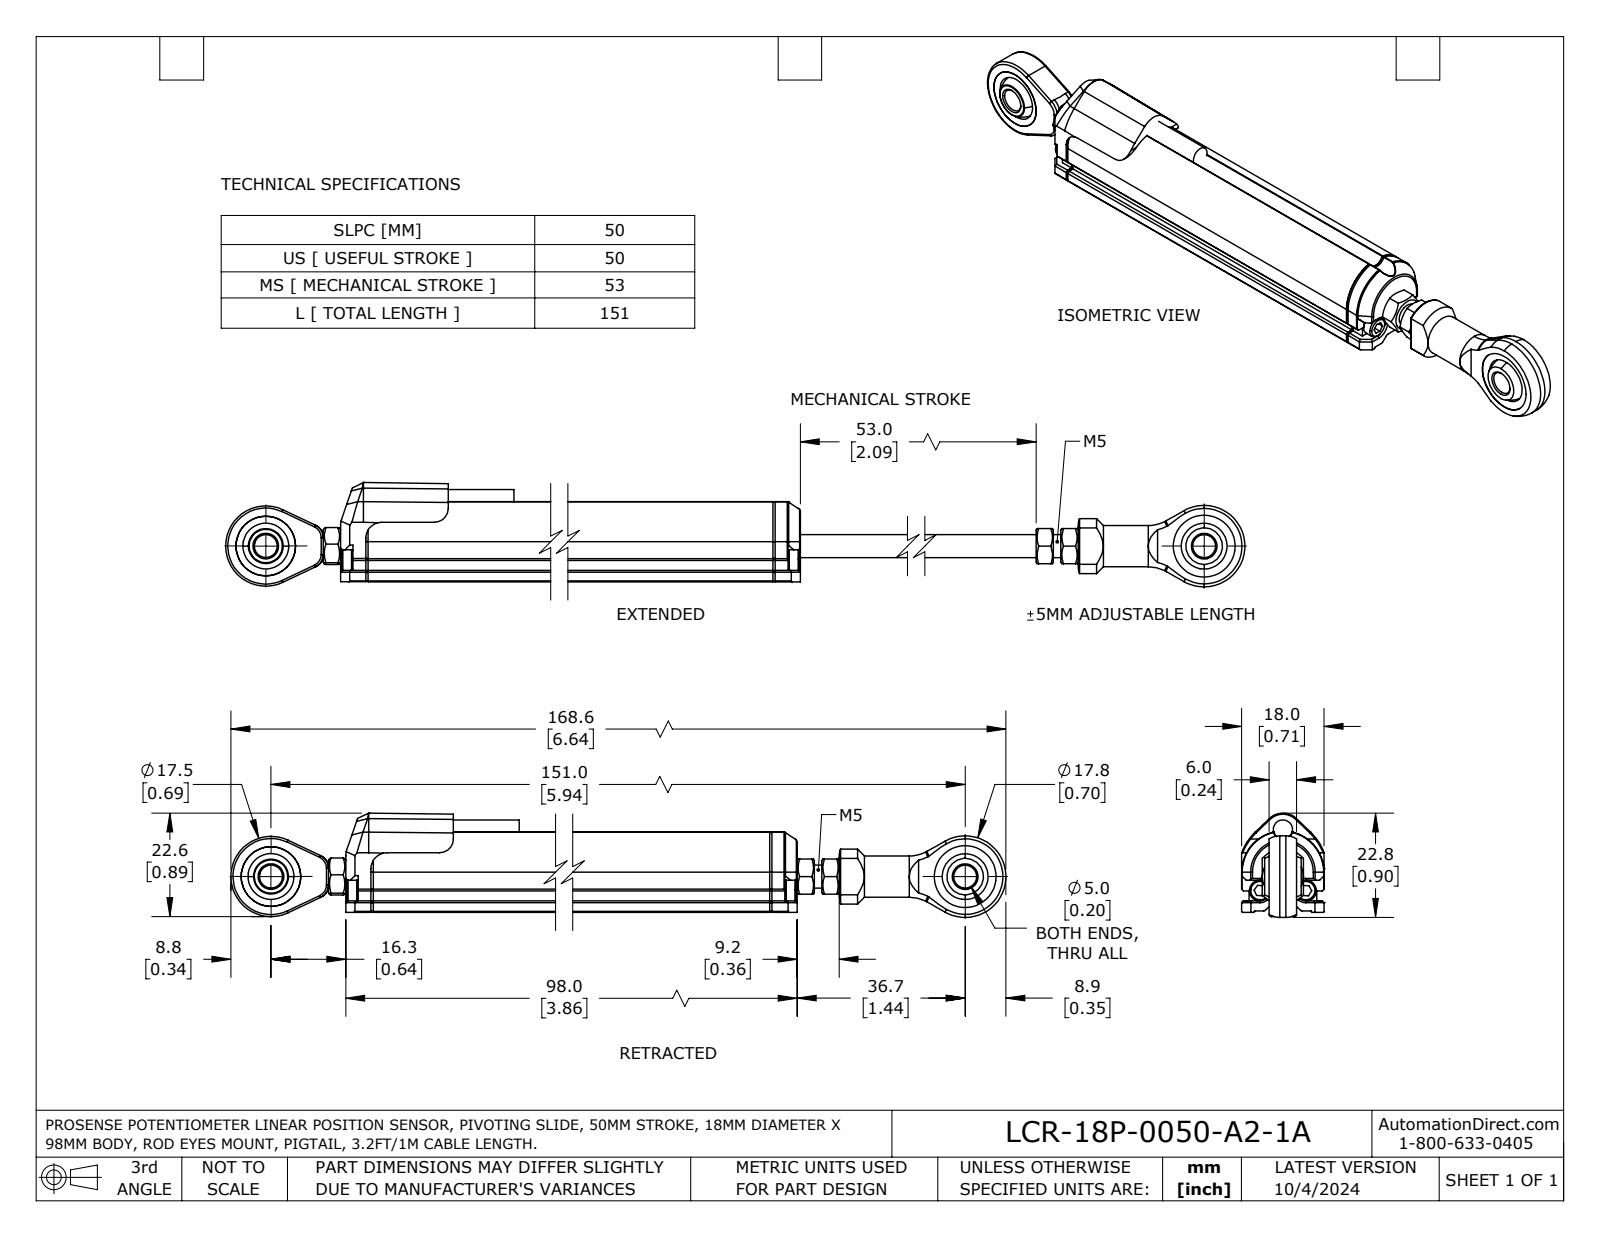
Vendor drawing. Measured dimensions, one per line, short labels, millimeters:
name: LCR-18P-0050-A2-1A
written by: SolidWorks 2023 (AUTOMOTIVE_DESIGN)
unit: mm
bodies: 20 solids, 515 faces (289 planar, 136 cylindrical, 90 other)
size: 168.7 × 22.8 × 18
volume: 32 330 mm³; area: 18 440 mm²
holes: 4× ⌀5, 2× ⌀2.6, 2× ⌀2.6, 2× ⌀10, 1× ⌀5.4, 1× ⌀6.9, 1× ⌀13, 1× ⌀13.5
bosses: 4× ⌀4.6, 3× ⌀2.9, 2× ⌀1.5, 1× ⌀9, 1× ⌀4.2, 1× ⌀2.9
rounds: 12× R0.2, 10× R0.1, 8× R0.5, 6× R0.3, 6× R0.5, 4× R0.4, 4× R1, 4× R1.1
face distances: 0.5, 86.5, 6, 18, 86, 1.5, 87, 12, 1.8, 4.4
hole spacings: 5.9, 10, 5.8, 5.9, 151
